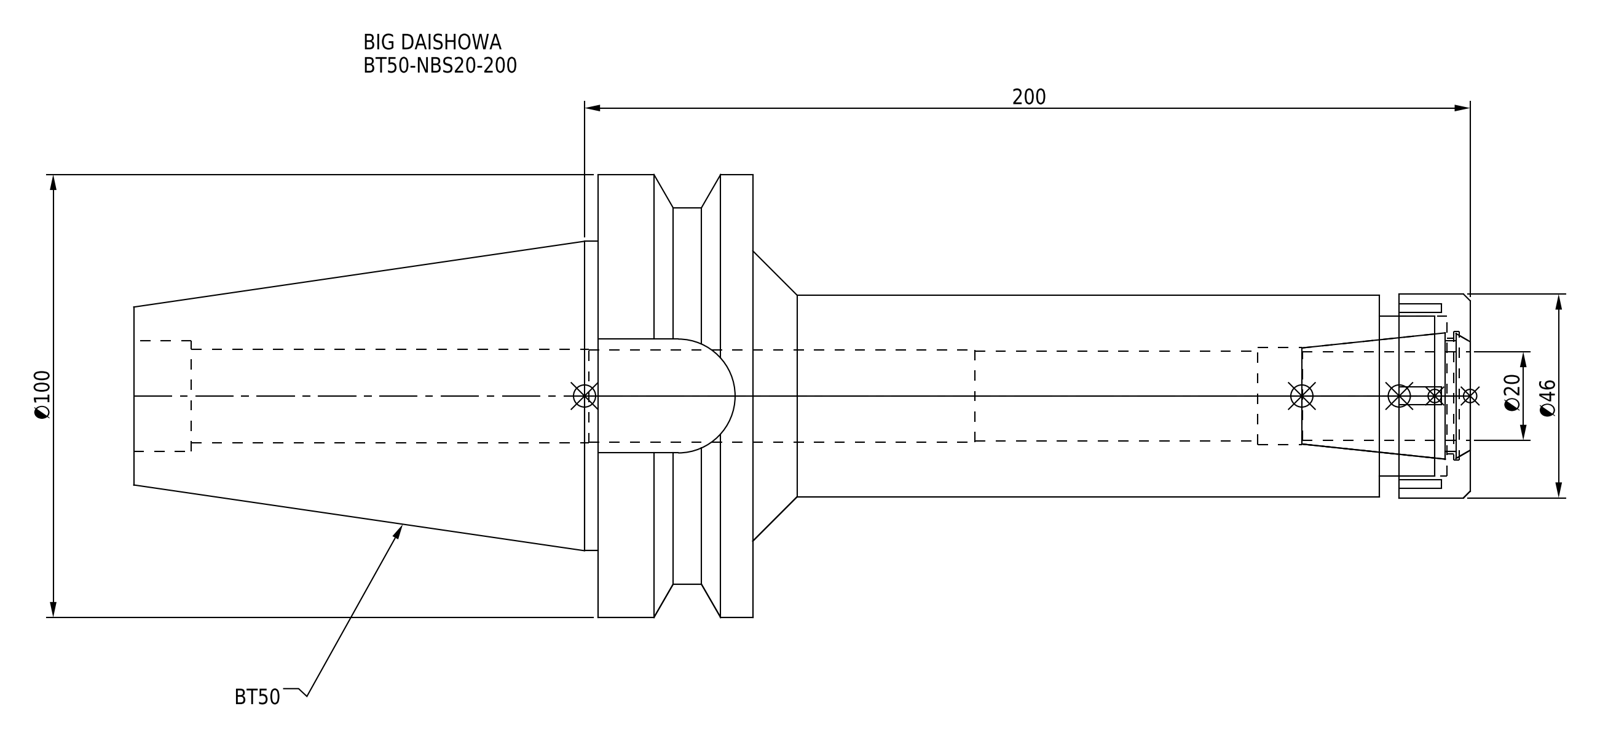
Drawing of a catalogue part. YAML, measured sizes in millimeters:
part_name: "BT50-NBS20-200_1.stp; DXF_TEMP_ASSY_ASM_4_ASM.stp; BT50-NBS20-200.stp; NBN20_1.stp (+3 more)"
step_written_by: "SolidWorks 2019 (CONFIG_CONTROL_DESIGN)"
units: millimeters
bodies: {solids: 2, faces: 93, planar: 45, cylindrical: 34, other: 14}
overall_size: [301.8, 100, 100]
volume: 650088
surface_area: 91736
round_holes:
  - {diameter: 20.3, count: 1}
  - {diameter: 20.8, count: 1}
  - {diameter: 21.2, count: 1}
  - {diameter: 22, count: 1}
  - {diameter: 25, count: 1}
  - {diameter: 26, count: 1}
  - {diameter: 29, count: 1}
  - {diameter: 36, count: 1}
round_bosses_or_shafts:
  - {diameter: 100, count: 1}
  - {diameter: 85, count: 1}
  - {diameter: 69.85, count: 1}
  - {diameter: 46, count: 1}
  - {diameter: 45.5, count: 1}
partial_cylinders:
  - {radius: 12.85, count: 1}
face_to_face_distances: [35, 162, 197, 8, 301.8, 139.8, 104.8, 70.8, 20.5, 141.5]
